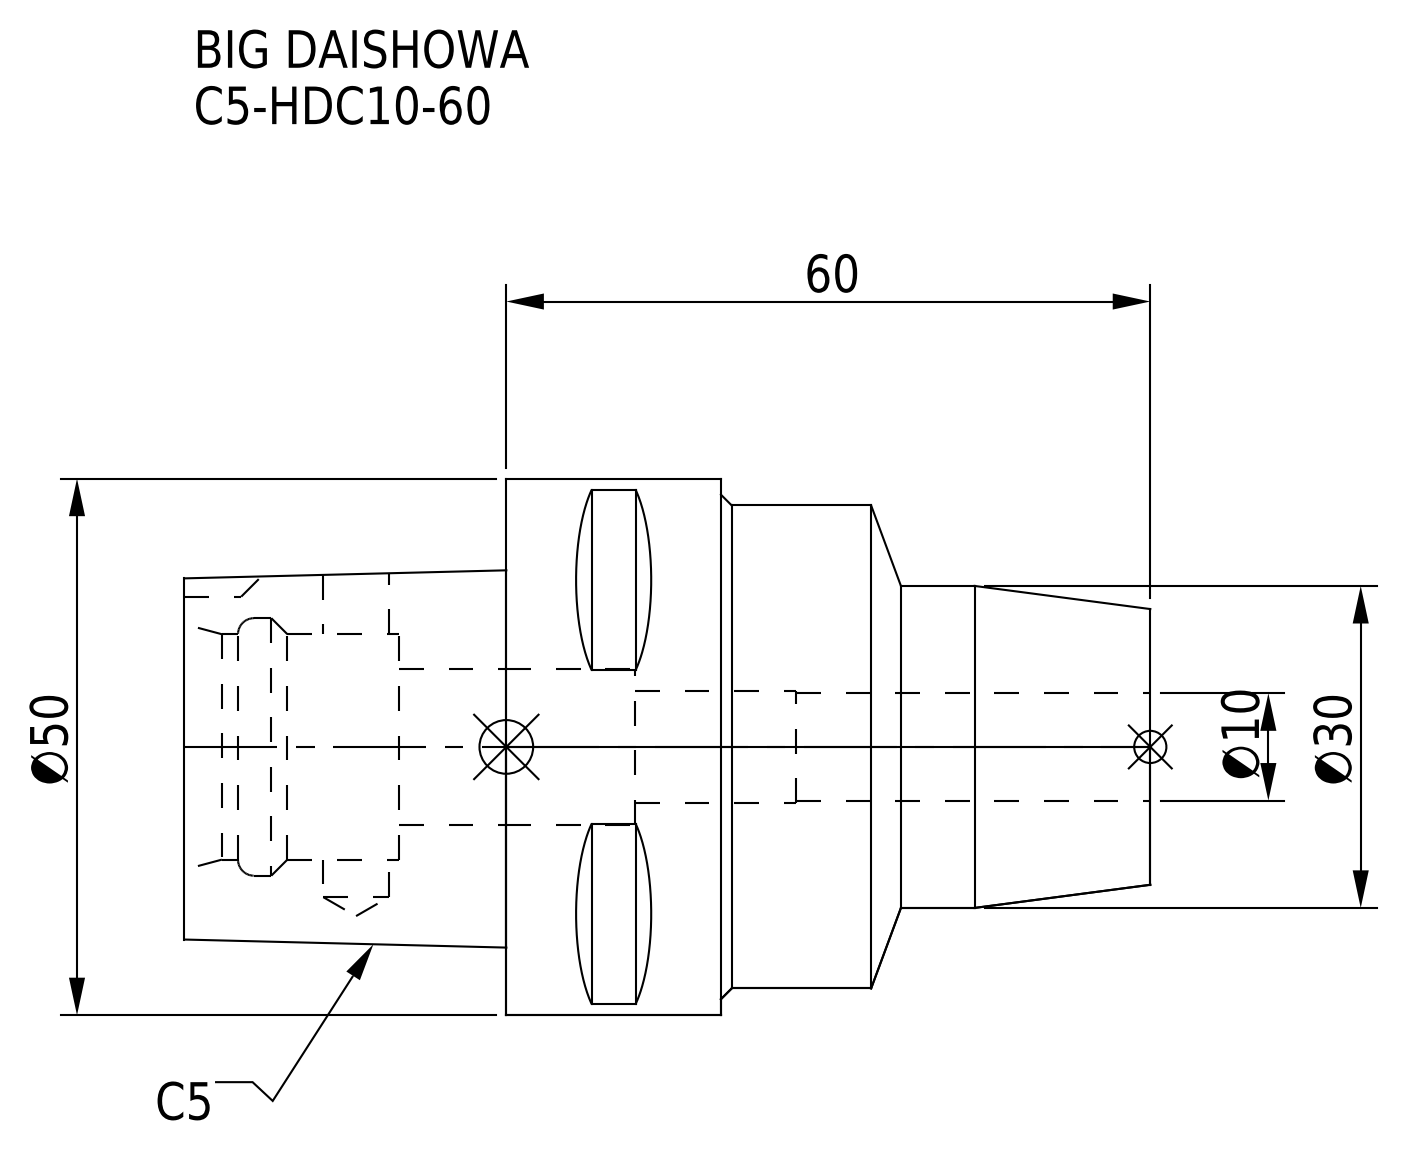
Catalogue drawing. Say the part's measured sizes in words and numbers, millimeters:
The part is named "C5-HDC10-60". Its 3-D file was written by "CREO PARAMETRIC BY PTC INC, 2016380 (AUTOMOTIVE_DESIGN)". It is 1 solid with 68 faces: 29 planar, 23 cylindrical and 16 other. Overall it measures 90 by 50 by 50 millimeters. Its volume is 90 870 cubic millimeters and its surface area 18 207 square millimeters. Round holes: 1 of diameter 6.1, 1 of diameter 10, 1 of diameter 10.5, 1 of diameter 14.5, 1 of diameter 21, 1 of diameter 24. Round bosses or shafts: 1 of diameter 50, 1 of diameter 45, 1 of diameter 30. Partial cylindrical surfaces (rounded edges, fillets, slot ends): 1 of radius 4. The main face-to-face distances are 30, 60, 20, 90, 40, 50, 44, 70, 10, 19.18.
